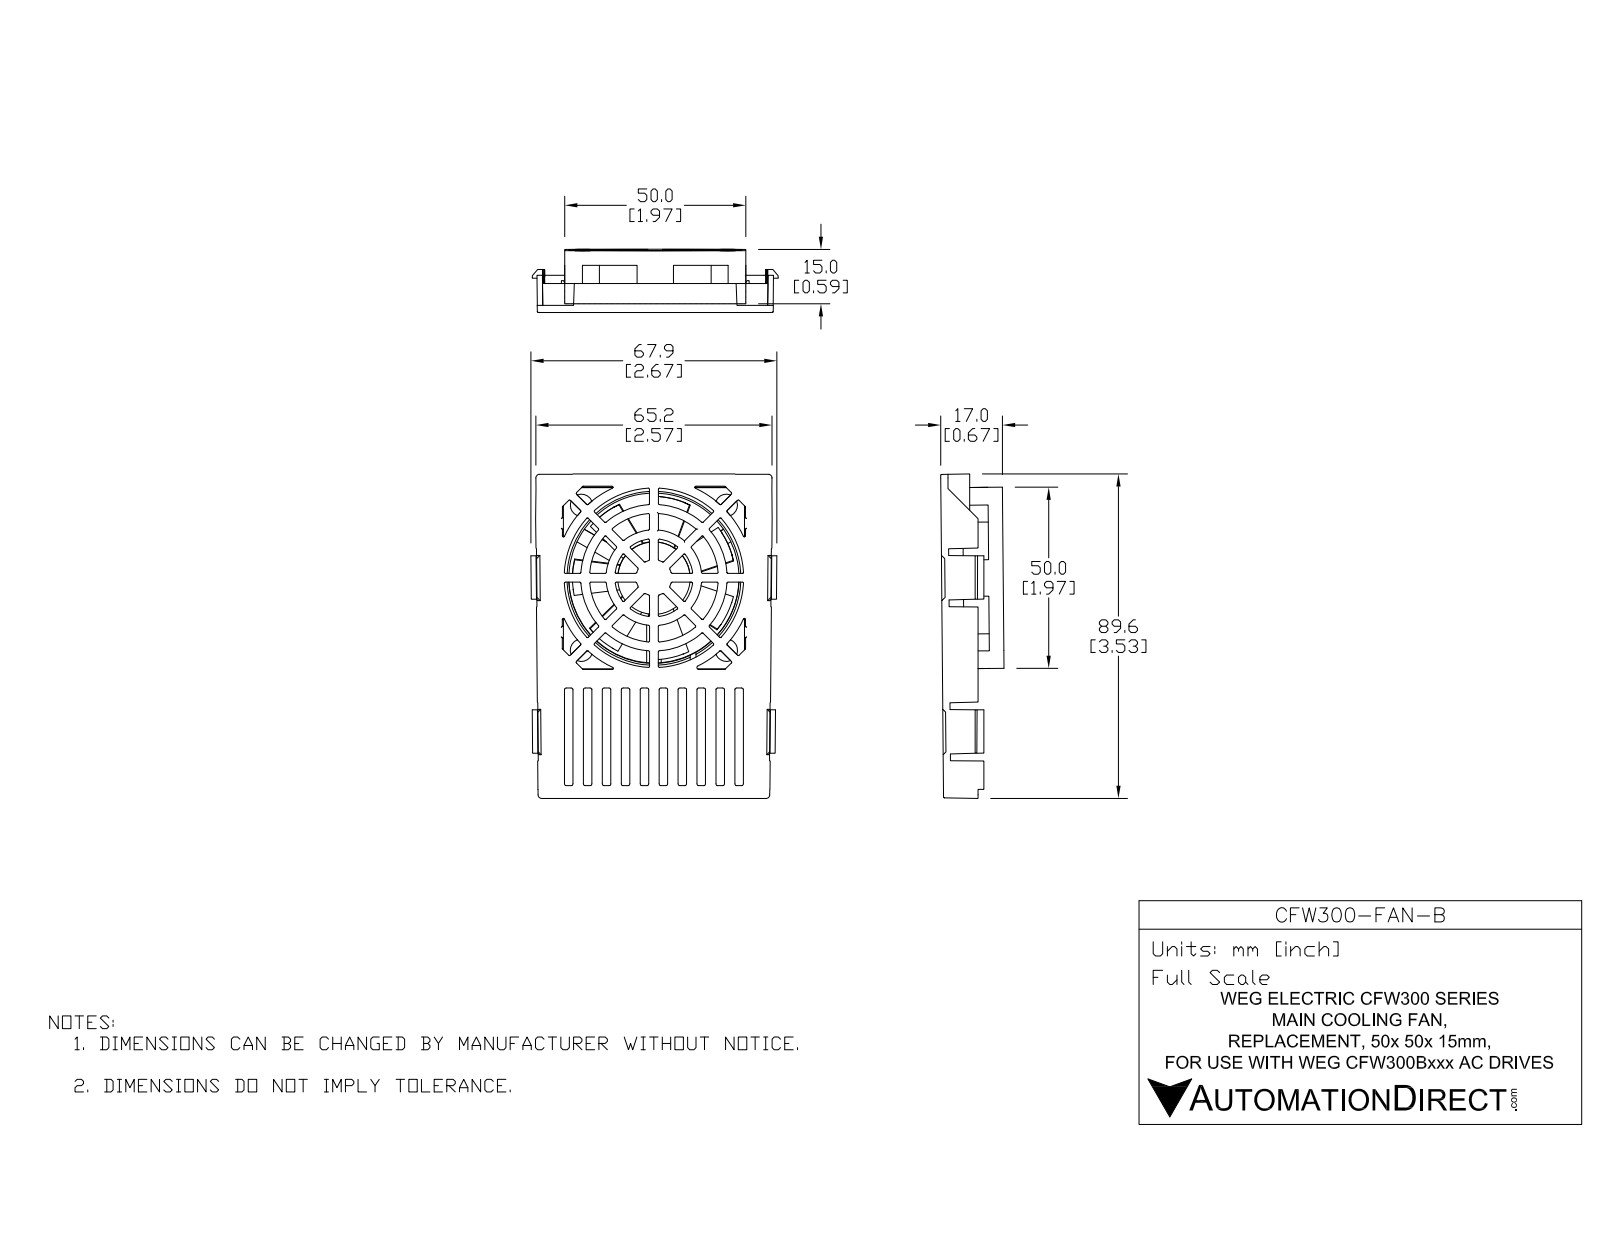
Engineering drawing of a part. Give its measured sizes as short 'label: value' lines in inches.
name: 113771364
written by: SolidWorks 2017 (AUTOMOTIVE_DESIGN)
unit: in
bodies: 2 solids, 1180 faces (394 planar, 267 cylindrical, 519 other)
size: 3.526 × 2.673 × 0.688
volume: 1.527 in³; area: 44.1 in²
holes: 4× ⌀0.169, 1× ⌀1.85
bosses: 1× ⌀0.984, 1× ⌀0.787
rounds: 65× R0.012, 46× R0.02, 4× R0.039, 4× R0.197, 1× R0.886, 1× R1.004
face distances: 0.079, 0.059, 0.591, 0.669, 1.969, 0.206, 0.511, 0.823, 0.617, 0.412
hole spacings: 1.113, 1.575, 2.227
